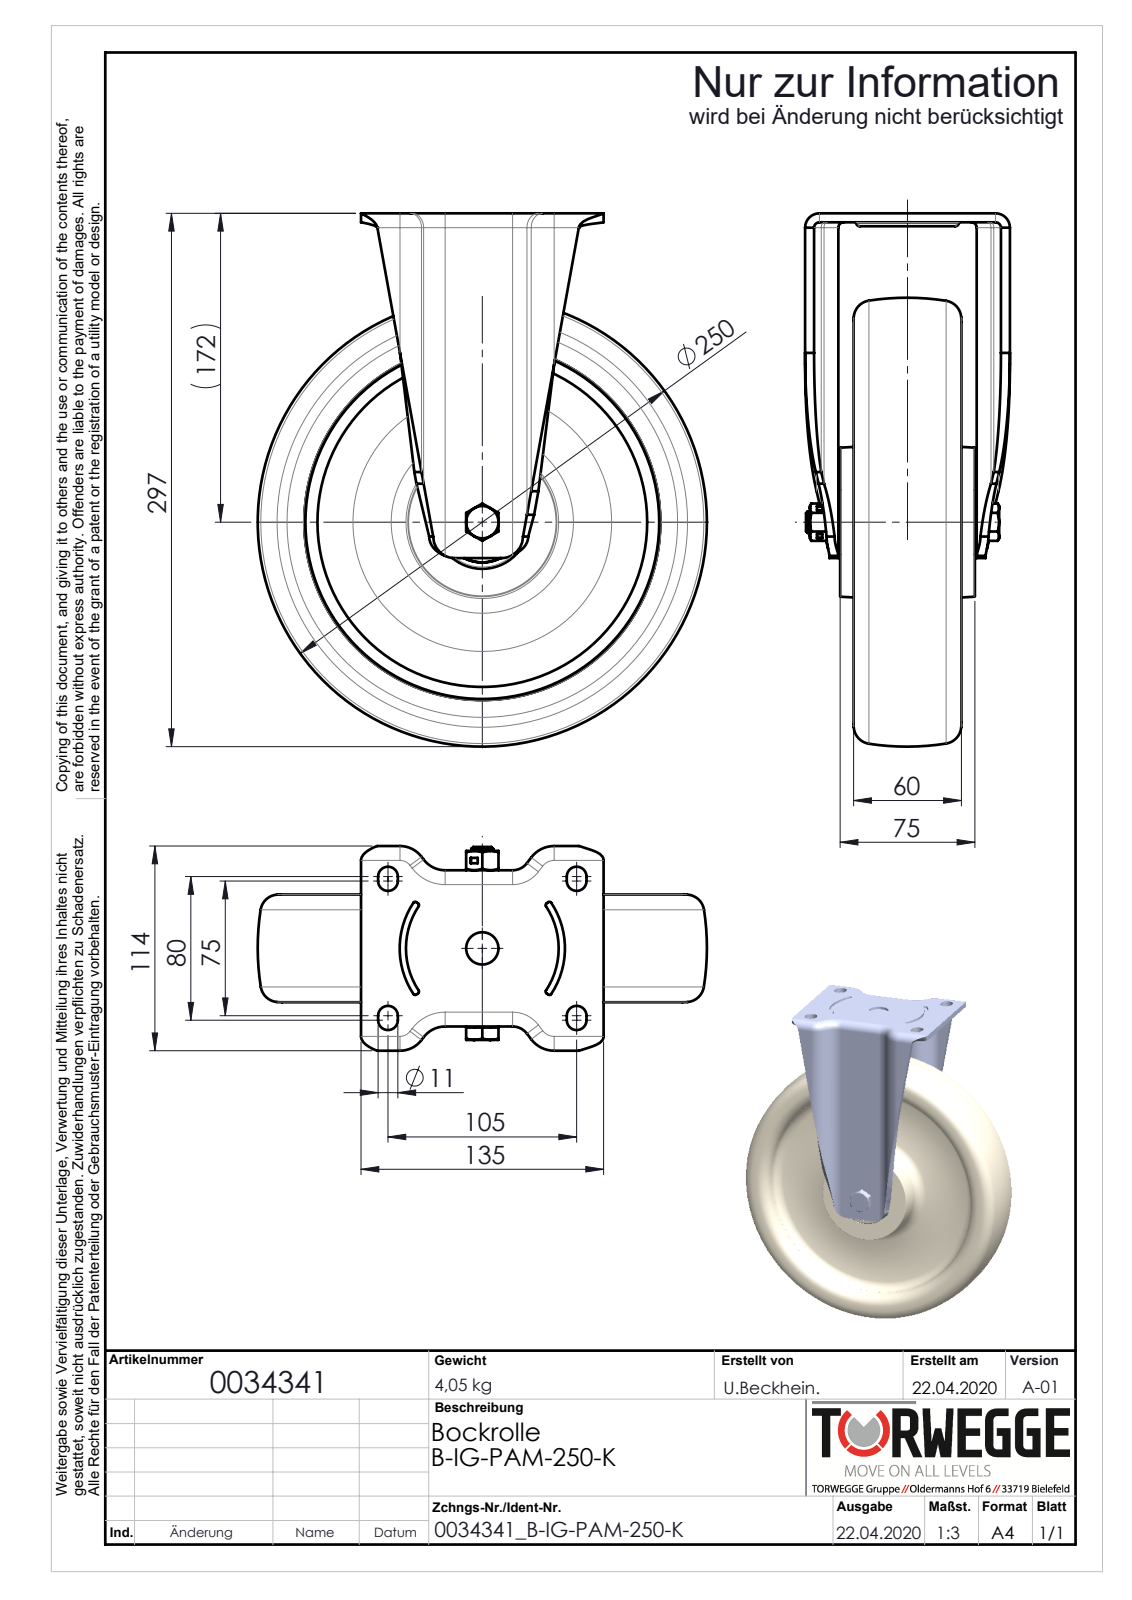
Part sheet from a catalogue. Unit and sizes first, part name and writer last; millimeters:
Units: millimetres
Overall size (bounding box): 297 × 250 × 114
Round holes (diameter × count): ⌀10.2 ×1, ⌀12 ×1, ⌀12.1 ×1, ⌀12.5 ×1, ⌀18 ×1, ⌀25 ×1, ⌀32.16 ×1, ⌀35 ×1, ⌀43.2 ×1, ⌀44.85 ×1, ⌀52 ×1
Round bosses / shafts (diameter × count): ⌀36 ×1, ⌀33.8 ×1, ⌀24.95 ×1, ⌀18 ×1
Partial cylindrical surfaces — rounded edges, fillets, slot ends (radius × count): R2.1 ×12, R1.1 ×8, R3 ×8, R5.5 ×8, R8 ×8, R15 ×6, R10 ×4, R11 ×2
Main face-to-face distances: 5, 82, 6, 81, 1, 76, 87, 77, 60, 21
Volume: 2 083 000 mm³ · Surface area: 315 772 mm²
Bodies: 16 solids, 464 faces (130 planar, 174 cylindrical, 160 other)
Part name (STEP PRODUCT): 0034341
STEP written by: SolidWorks 2018 (AUTOMOTIVE_DESIGN)
